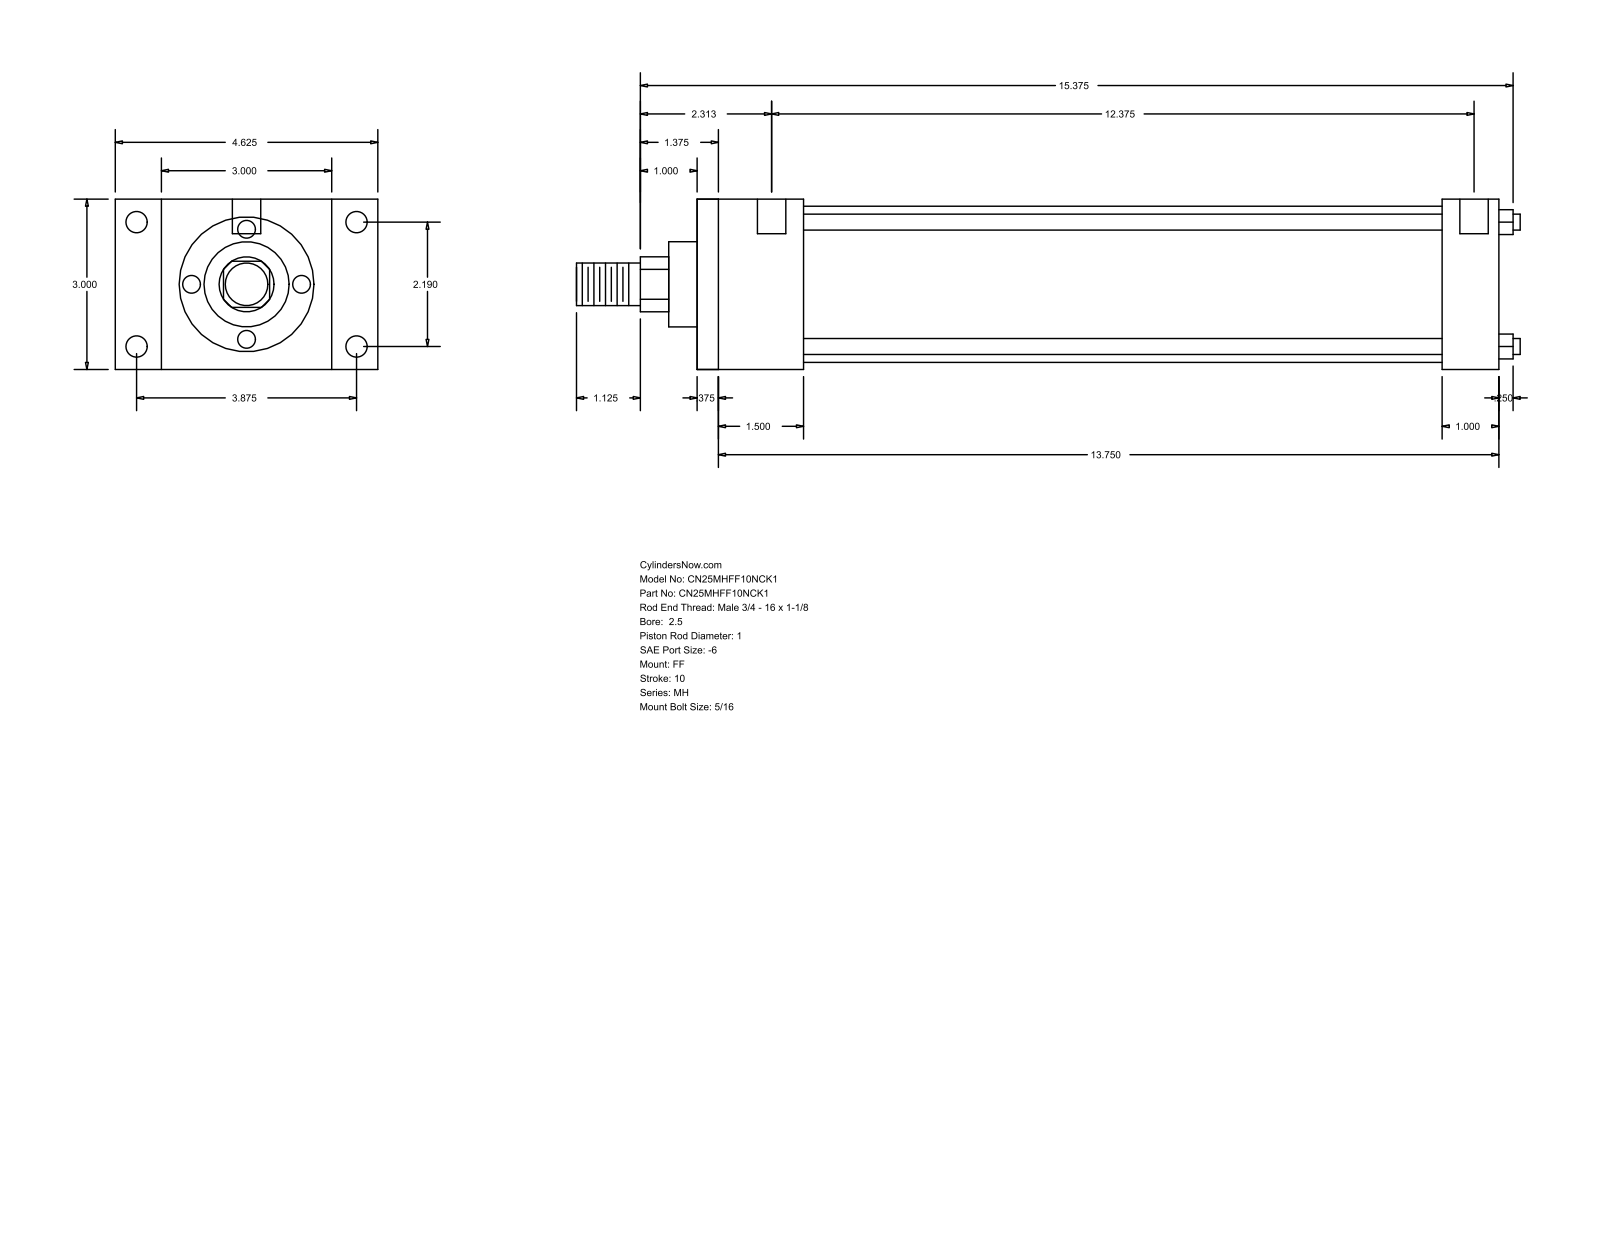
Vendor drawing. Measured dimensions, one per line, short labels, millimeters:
name: MH_FF__0250_1
written by: GSSL Pune (CONFIG_CONTROL_DESIGN)
unit: mm
bodies: 0 solids, 92 faces (64 planar, 28 cylindrical, 0 other)
size: 422.27 × 117.47 × 76.2
holes: 4× ⌀5.56, 4× ⌀9.53, 2× ⌀12.7
bosses: 4× ⌀7.14, 1× ⌀69.85, 1× ⌀38.1, 1× ⌀25.4, 1× ⌀19.05
rounds: 1× R12.29
face distances: 76.2, 358.78, 9.52, 349.26, 47.63, 333.37, 38.11, 323.85, 285.74, 311.15
hole spacings: 55.62, 98.42, 113.05, 322.26, 3.18, 4.76, 314.32, 317.5
